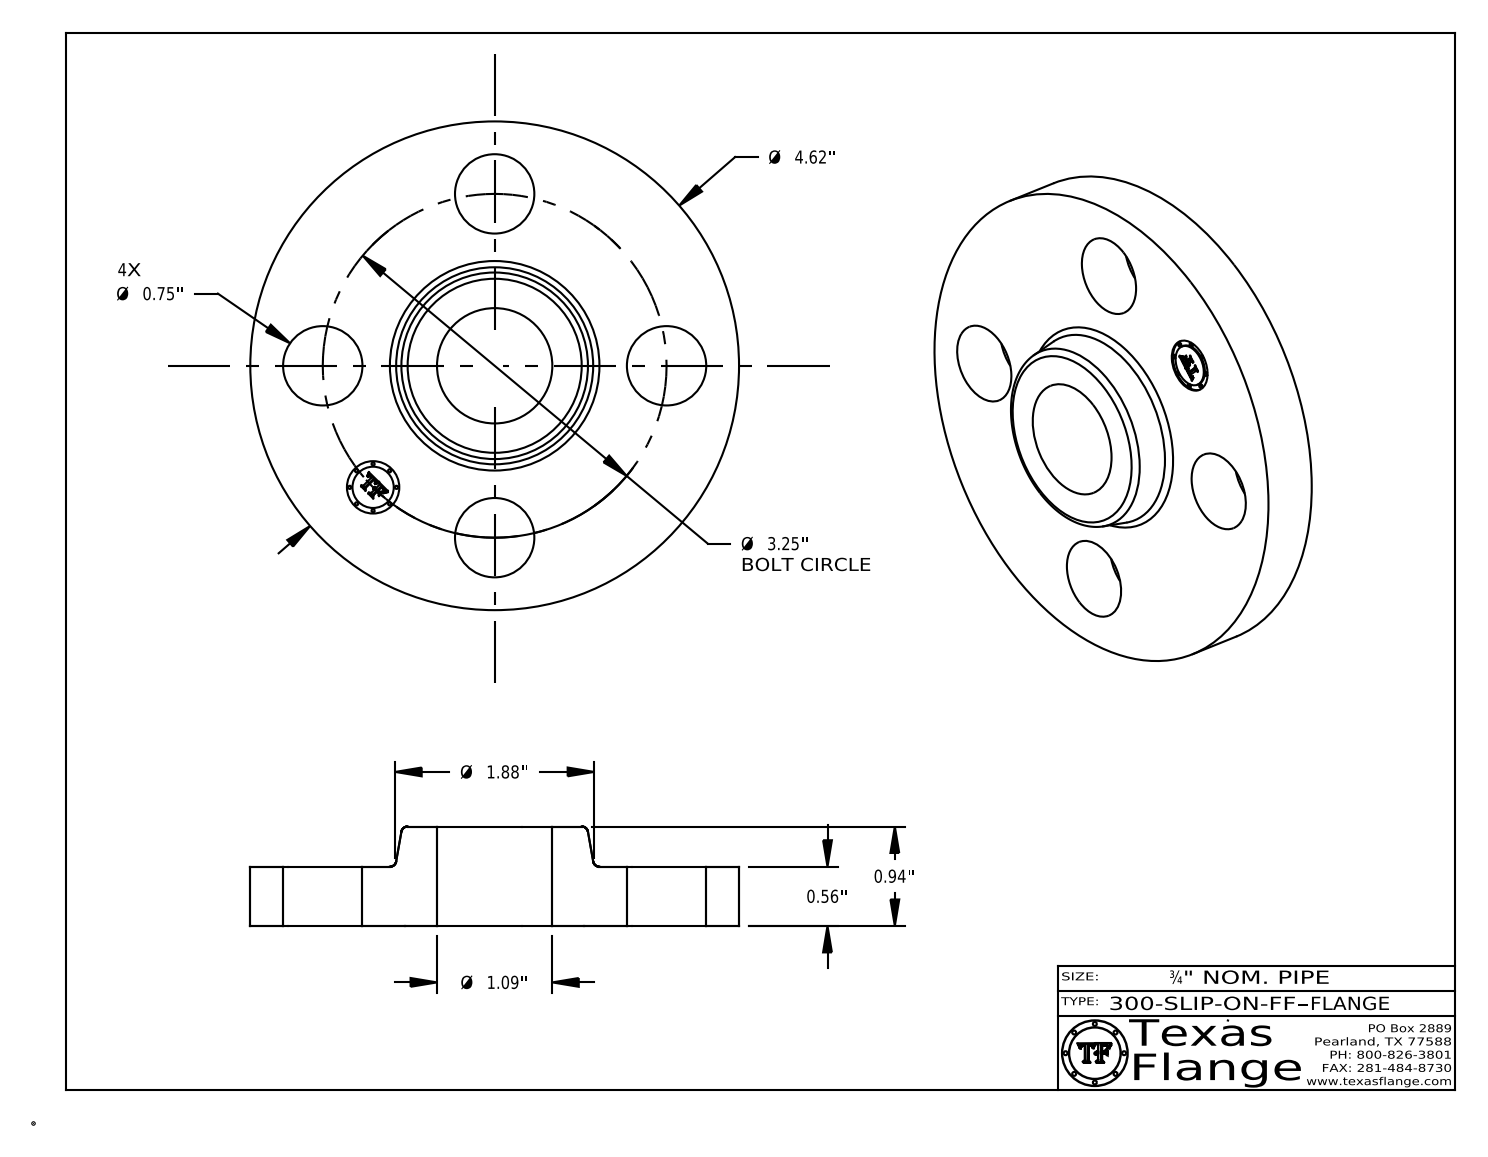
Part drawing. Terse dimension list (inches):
name: 300-SLIP-ON-FF
written by: CATIA V5 STEP AP214 (AUTOMOTIVE_DESIGN)
unit: in
bodies: 1 solid, 407 faces (369 planar, 32 cylindrical, 6 other)
size: 4.62 × 4.62 × 0.94
volume: 8.502 in³; area: 46.47 in²
holes: 4× ⌀0.75, 1× ⌀0.495, 1× ⌀1.09
bosses: 8× ⌀0.03, 1× ⌀4.62, 1× ⌀0.39
face distances: 0.56, 0.94, 0.38, 0.545, 0.015, 0.395, 0.148, 0.144, 0.027, 0.096
hole spacings: 1.625, 2.298, 1.244, 3.003, 3.25
